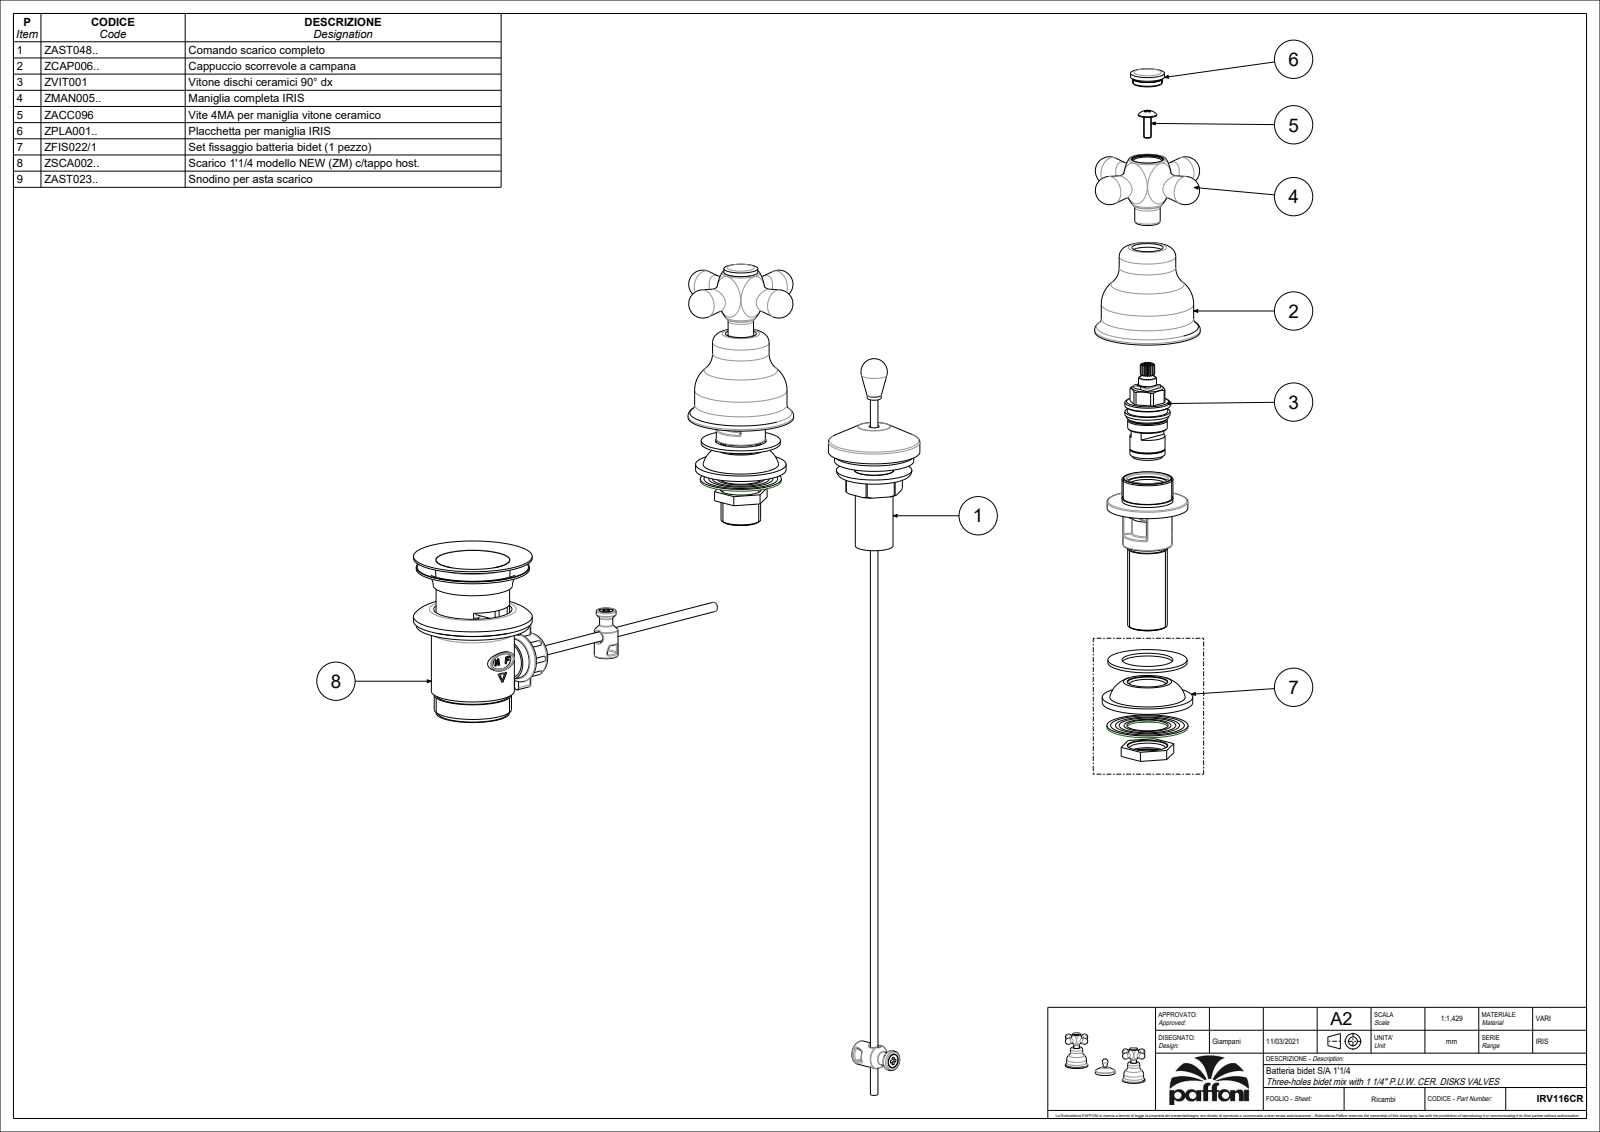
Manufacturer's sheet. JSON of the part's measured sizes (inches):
{"part_name": "IRV116CR", "step_written_by": "CREO PARAMETRIC BY PTC INC, 2020044 (CONFIG_CONTROL_DESIGN)", "units": "inches", "bodies": {"solids": 4, "faces": 158, "planar": 10, "cylindrical": 26, "other": 122}, "overall_size": [10.709, 3.276, 2.835], "volume_in3": 11.35, "surface_area_in2": 56.02, "round_holes": [[0.217, 1]], "round_bosses_or_shafts": [[2.165, 2], [1.929, 2], [1.102, 2], [0.709, 2], [0.531, 2], [1.909, 1], [0.197, 1]], "face_to_face_distances": [1.831, 0.551, 1.28, 3.138, 2.587, 1.307, 0.63, 0.079, 1.201, 2.508]}
